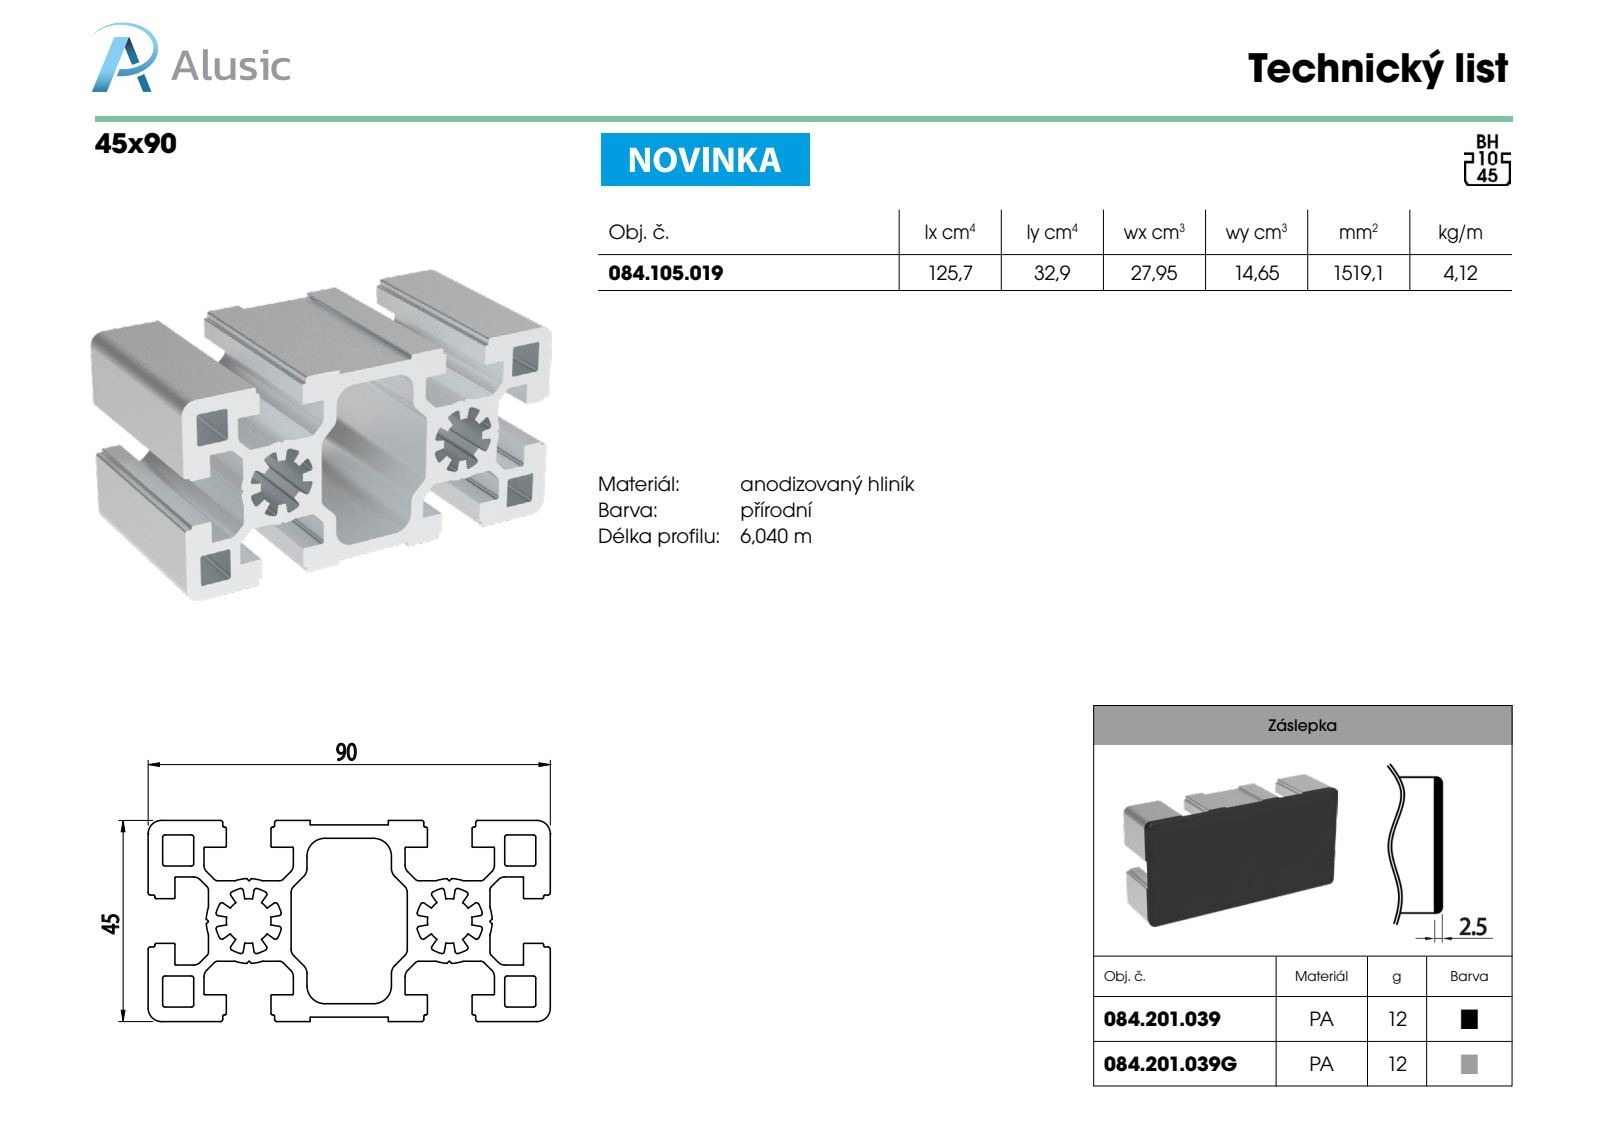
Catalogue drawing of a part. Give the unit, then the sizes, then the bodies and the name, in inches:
Units: inches
Overall size (bounding box): 3.937 × 3.543 × 1.772
Partial cylindrical surfaces — rounded edges, fillets, slot ends (radius × count): R0.02 ×60, R0.004 ×26, R0.008 ×24, R0.012 ×24, R0.039 ×24, R0.079 ×16, R0.098 ×4, R0.118 ×4
Main face-to-face distances: 1.772, 0.531, 0.236, 0.089, 0.362, 1.083, 0.157, 0.128, 0.402, 0.274
Volume: 9.234 in³ · Surface area: 143.8 in²
Bodies: 1 solid, 419 faces (176 planar, 243 cylindrical, 0 other)
Part name (STEP PRODUCT): 084.105.019
STEP written by: SolidWorks 2018 (AUTOMOTIVE_DESIGN)
